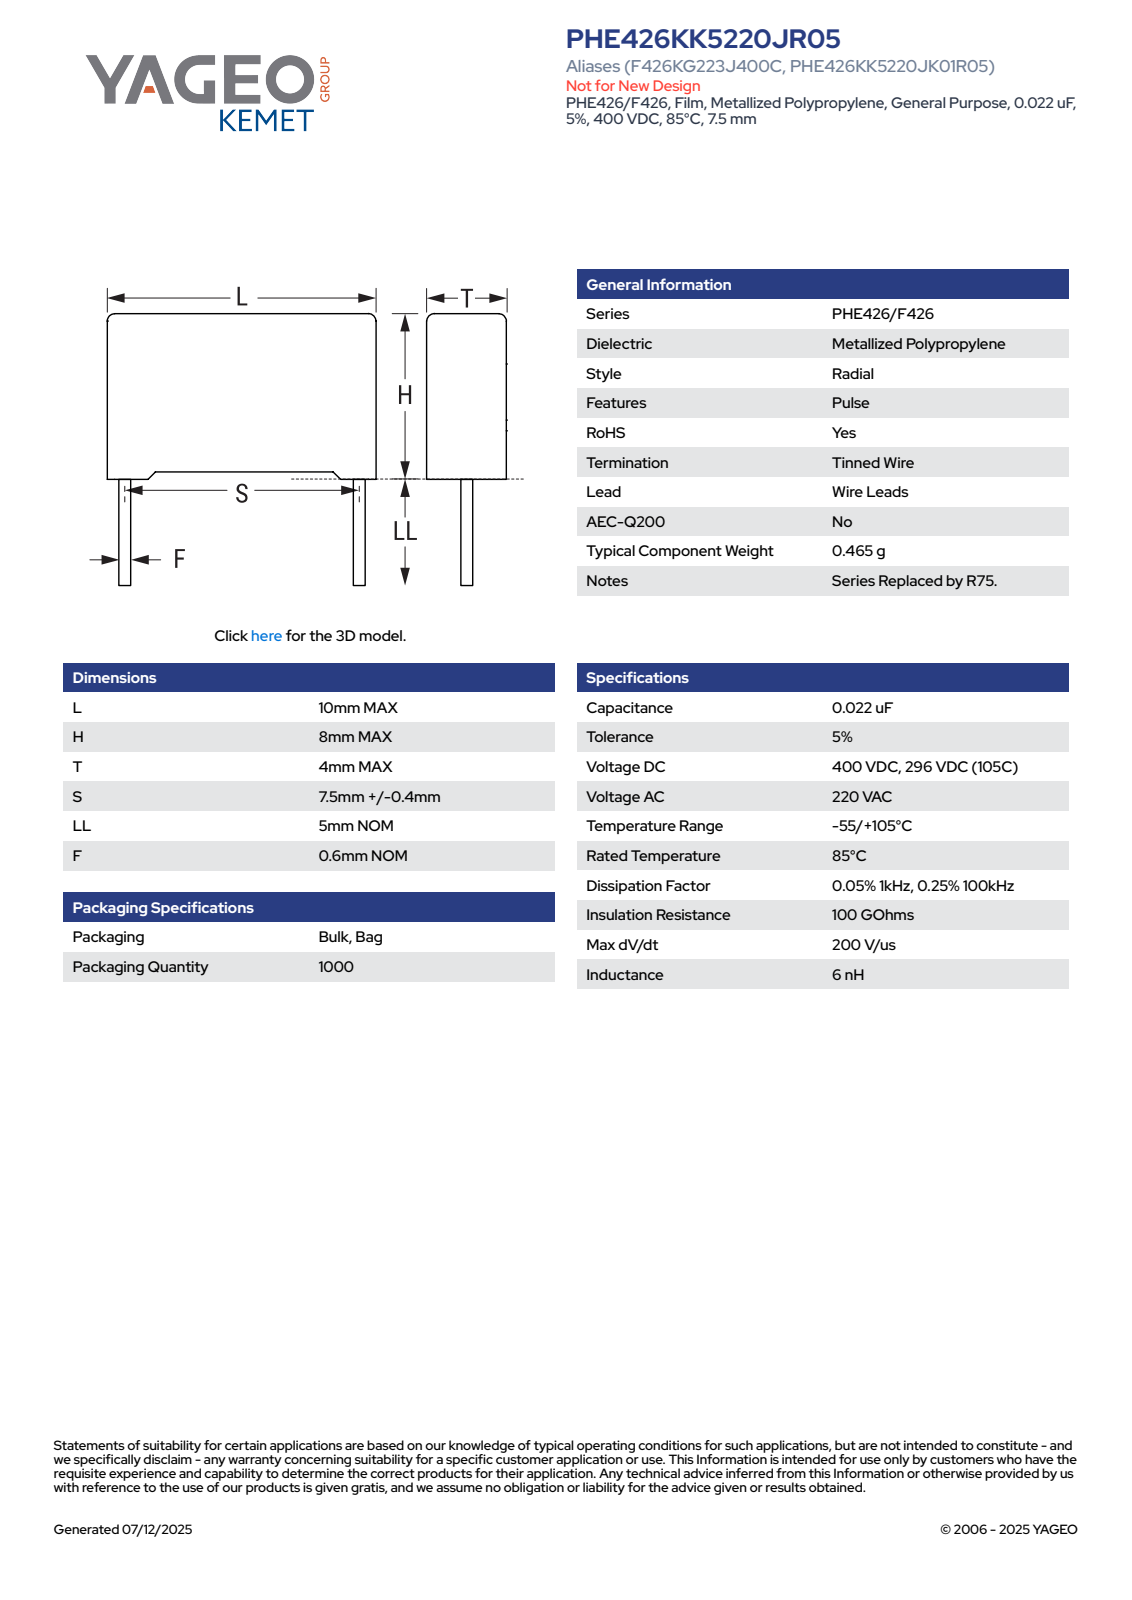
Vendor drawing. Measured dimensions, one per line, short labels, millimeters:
name: CFR_RB2_10X8X4_L10H8T4S7.5LL5F0.6
written by: SolidWorks 2021 (AUTOMOTIVE_DESIGN)
unit: mm
bodies: 4 solids, 85 faces (77 planar, 8 cylindrical, 0 other)
size: 13 × 10 × 4
volume: 298 mm³; area: 342 mm²
bosses: 2× ⌀0.6
rounds: 4× R0.5
face distances: 4, 10, 7.25, 0.33, 3.67, 0.75, 8, 3.34, 9.67, 0.47
